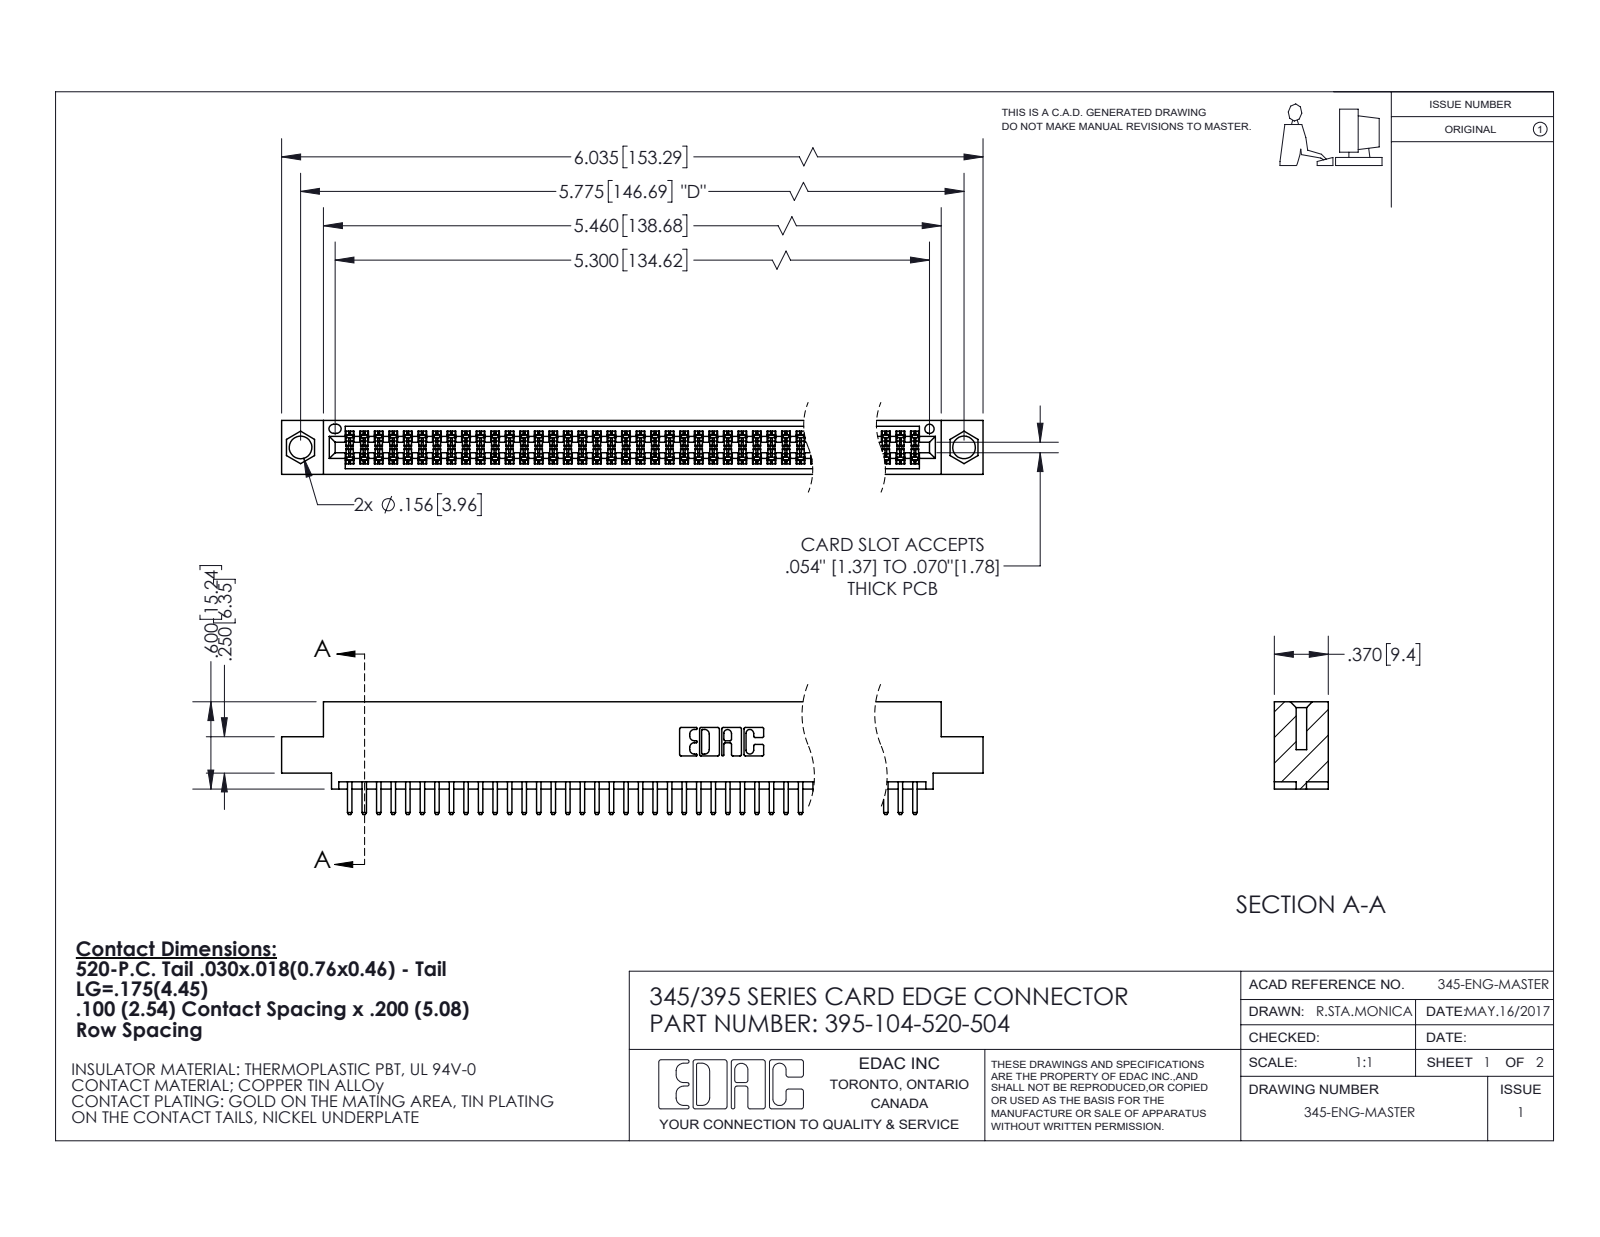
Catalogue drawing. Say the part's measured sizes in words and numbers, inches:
The part is named "345 Part_0.110 Offset - 0.156 Dia-TI; 345-292-001_345-293-120; 395-104-520-504". Its 3-D file was written by "SolidWorks 2020 (CONFIG_CONTROL_DESIGN)". It is 105 solids with 5760 faces: 3738 planar, 2022 cylindrical and 0 other. Overall it measures 6.035 by 0.775 by 0.37 inches. Its volume is 0.901 cubic inches and its surface area 33.88 square inches. Round holes: 2 of diameter 0.156, 1 of diameter 0.064. Partial cylindrical surfaces (rounded edges, fillets, slot ends): 156 of radius 0.006, 108 of radius 0.01, 22 of radius 0.01, 6 of radius 0.007, 6 of radius 0.031, 3 of radius 0.026, 2 of radius 0.014, 2 of radius 0.019. The main face-to-face distances are 0.298, 0.072, 0.2, 0.37, 0.098, 0.272, 0.025, 0.225, 0.022, 0.072. The hole center spacings are 0.27, 5.539, 5.775.
